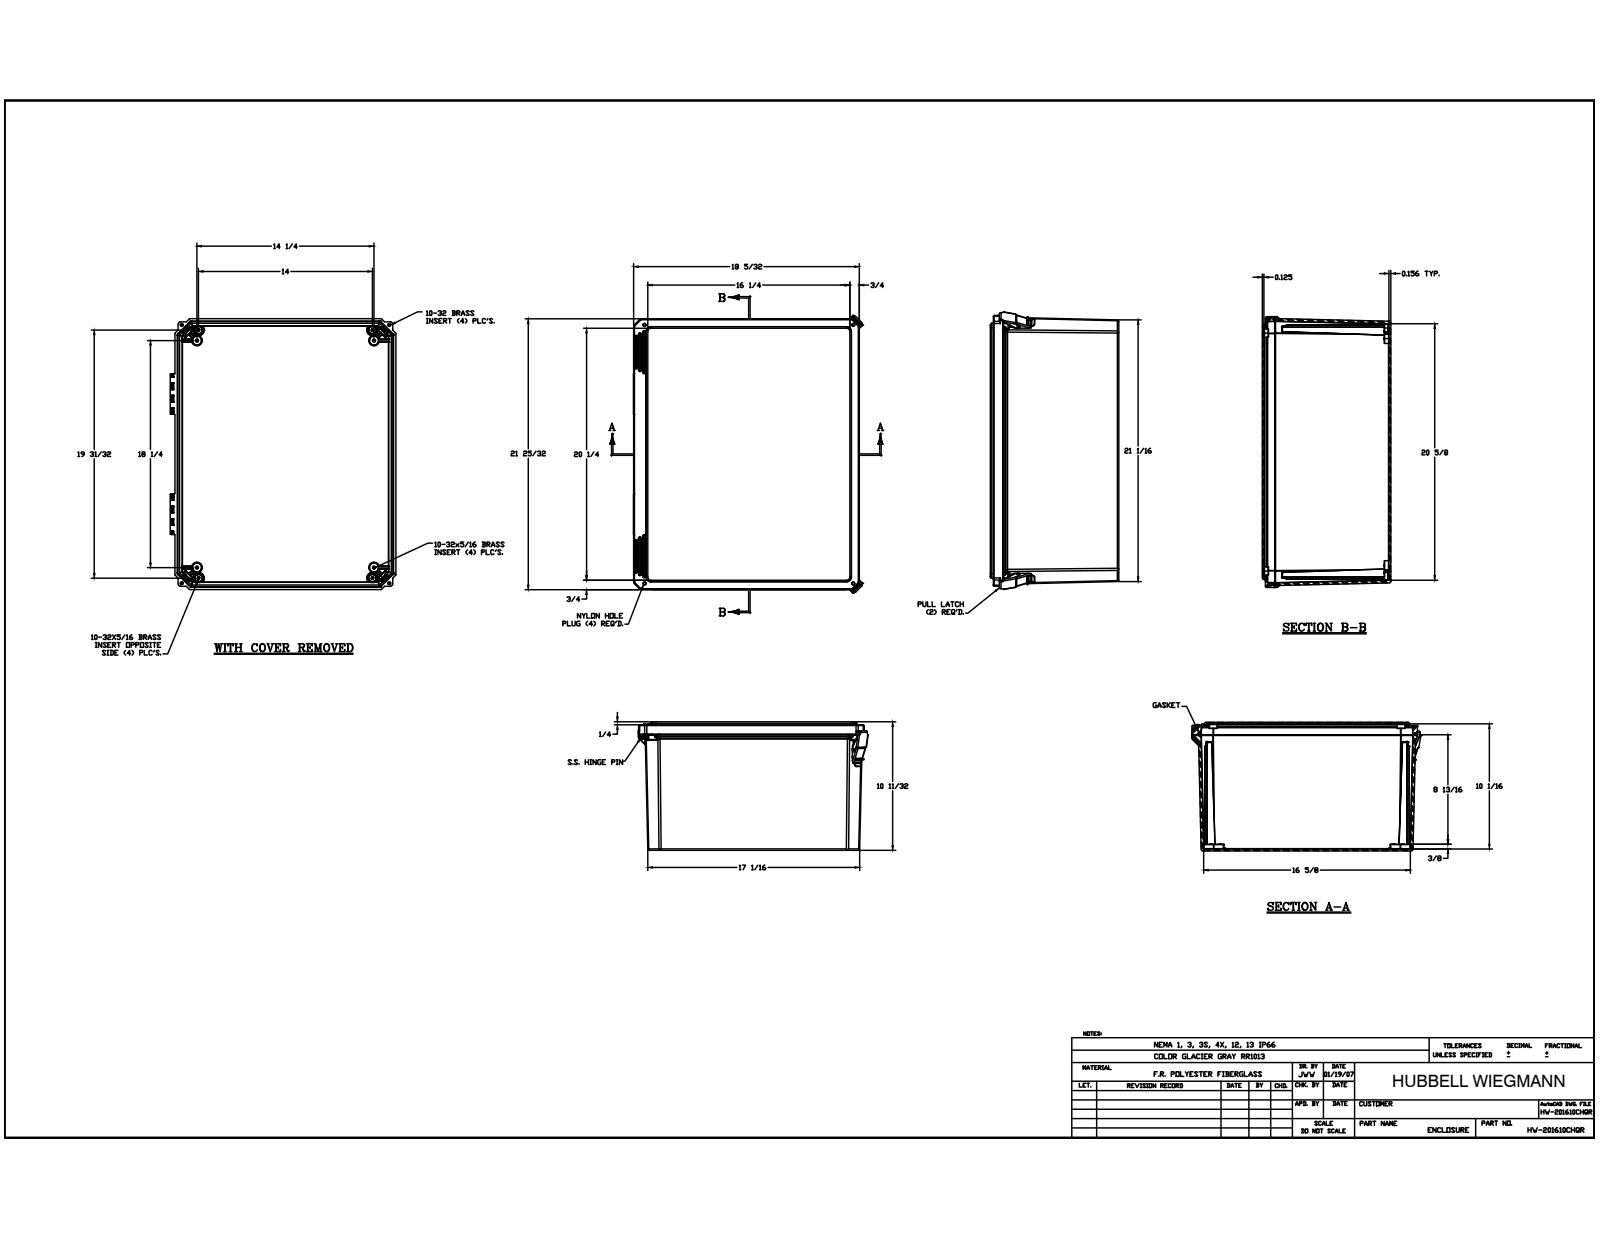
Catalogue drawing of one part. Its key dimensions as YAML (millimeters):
part_name: "DS201610BOX; BRASS INSERT-(; BRASS INSERT-(_1; BRASS INSERT-(_2 (+6 more)"
step_written_by: "Autodesk Inventor 2014 (AUTOMOTIVE_DESIGN)"
units: millimeters
bodies: {solids: 35, faces: 2602, planar: 908, cylindrical: 1046, other: 648}
overall_size: [568, 468.78, 262.67]
volume: 4688000
surface_area: 2073000
round_holes:
  - {diameter: 3.96, count: 16}
  - {diameter: 3.43, count: 9}
  - {diameter: 3.86, count: 8}
  - {diameter: 3.81, count: 4}
  - {diameter: 6.4, count: 4}
  - {diameter: 6.43, count: 4}
  - {diameter: 3.43, count: 2}
  - {diameter: 5.56, count: 2}
  - {diameter: 5.77, count: 2}
  - {diameter: 7.94, count: 2}
  - {diameter: 9.52, count: 2}
  - {diameter: 3.48, count: 1}
round_bosses_or_shafts:
  - {diameter: 6.25, count: 16}
  - {diameter: 7.62, count: 4}
  - {diameter: 5.3, count: 4}
  - {diameter: 3.43, count: 3}
  - {diameter: 11.05, count: 1}
  - {diameter: 11.05, count: 1}
partial_cylinders:
  - {radius: 0.25, count: 212}
  - {radius: 0.51, count: 111}
  - {radius: 0.13, count: 88}
  - {radius: 0.76, count: 63}
  - {radius: 1.52, count: 34}
  - {radius: 1.59, count: 27}
  - {radius: 2.29, count: 26}
  - {radius: 0.76, count: 24}
face_to_face_distances: [3.17, 3.96, 258.71, 262.67, 259.5, 255.54, 5.38, 5.34, 6.35, 3.18]
hole_center_spacings: [6.35, 36.97, 405.96, 6.34, 359.42, 373.33, 395.52, 633.4]
